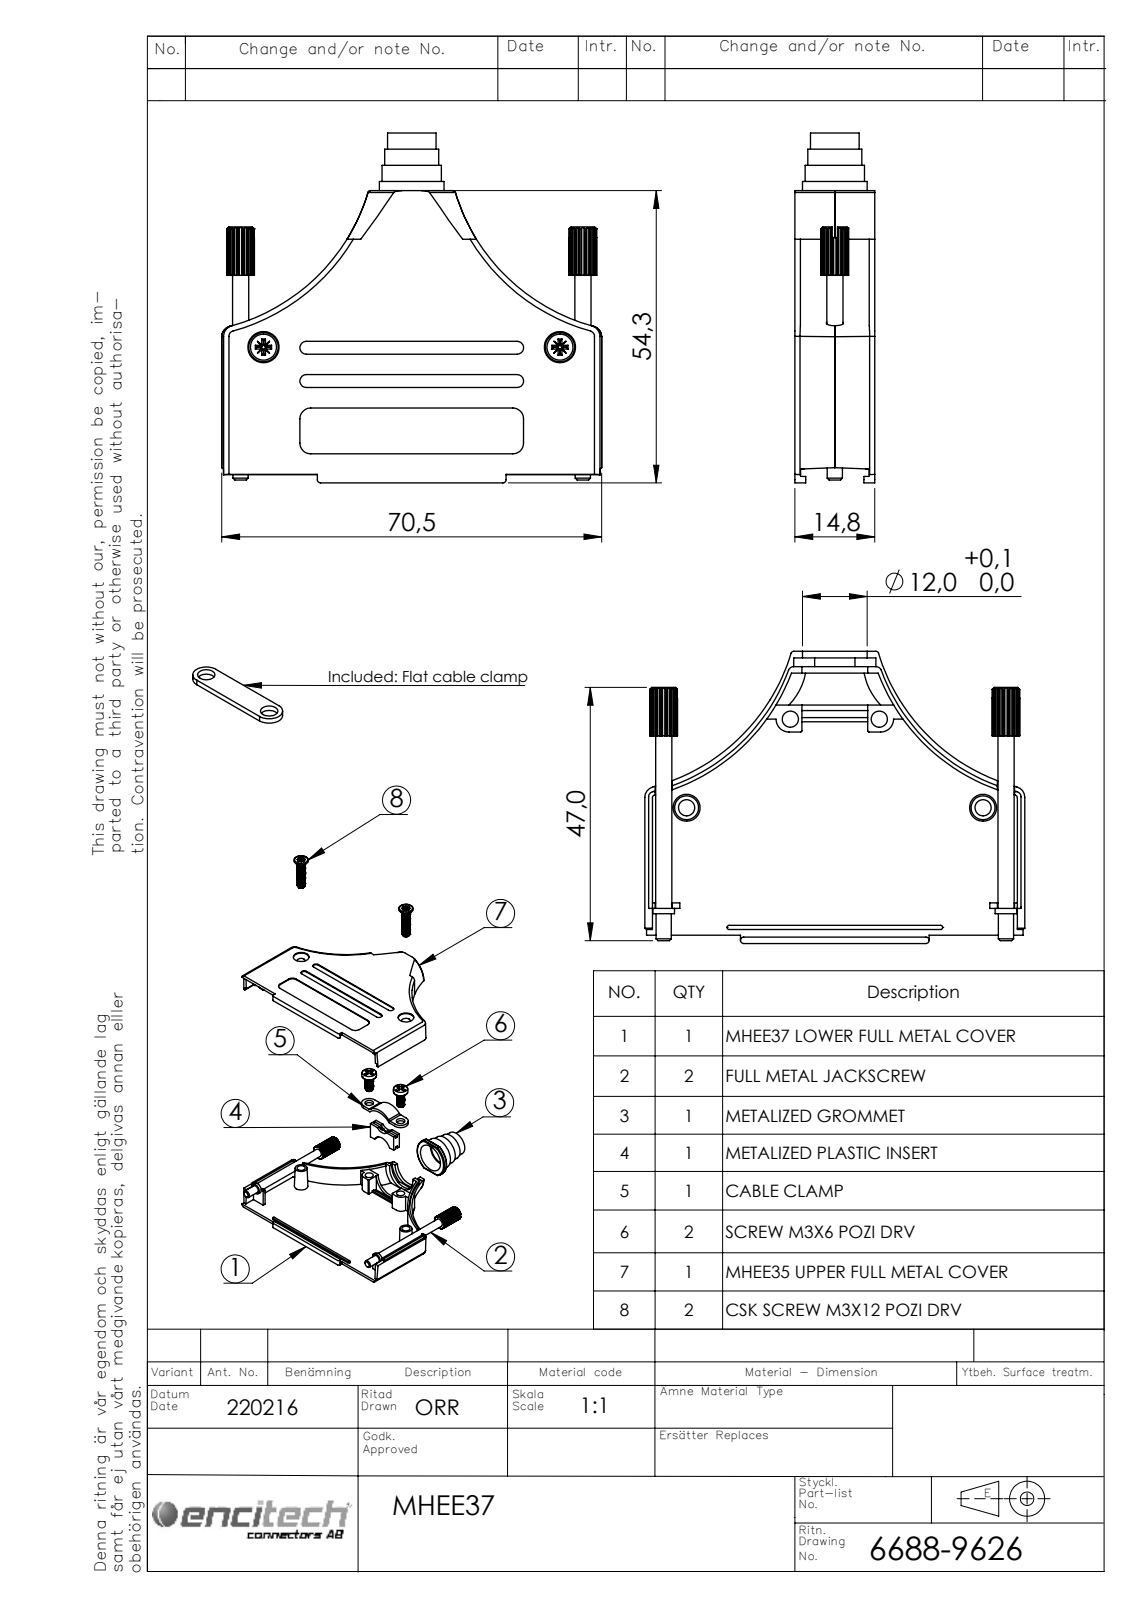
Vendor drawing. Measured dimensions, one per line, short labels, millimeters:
name: Plastic insert MHEE; 6805-0136-04; 6560-0137-04; 6830-0109-01 (+5 more)
written by: SolidWorks 2021 (AUTOMOTIVE_DESIGN)
unit: mm
bodies: 11 solids, 870 faces (420 planar, 342 cylindrical, 108 other)
size: 70.5 × 64.95 × 14.8
volume: 10 351 mm³; area: 20 310 mm²
holes: 4× ⌀3, 4× ⌀3.2, 2× ⌀4.5, 2× ⌀5.8, 1× ⌀3.3, 1× ⌀7.5, 1× ⌀8.5, 1× ⌀9.5, 1× ⌀10.5, 1× ⌀12, 1× ⌀12.2
bosses: 4× ⌀2.9, 2× ⌀4, 2× ⌀3, 2× ⌀2.8, 1× ⌀11, 1× ⌀10, 1× ⌀9
rounds: 14× R1, 8× R0.1, 7× R36.71, 4× R0.2, 4× R0.3, 4× R1.2, 4× R2, 3× R0.25
face distances: 13.75, 1.05, 12.7, 14.8, 0.75, 14.5, 13.45, 6.35, 7.1, 14.2
hole spacings: 25.32, 31.75, 39.35, 16.5, 55, 63.5
